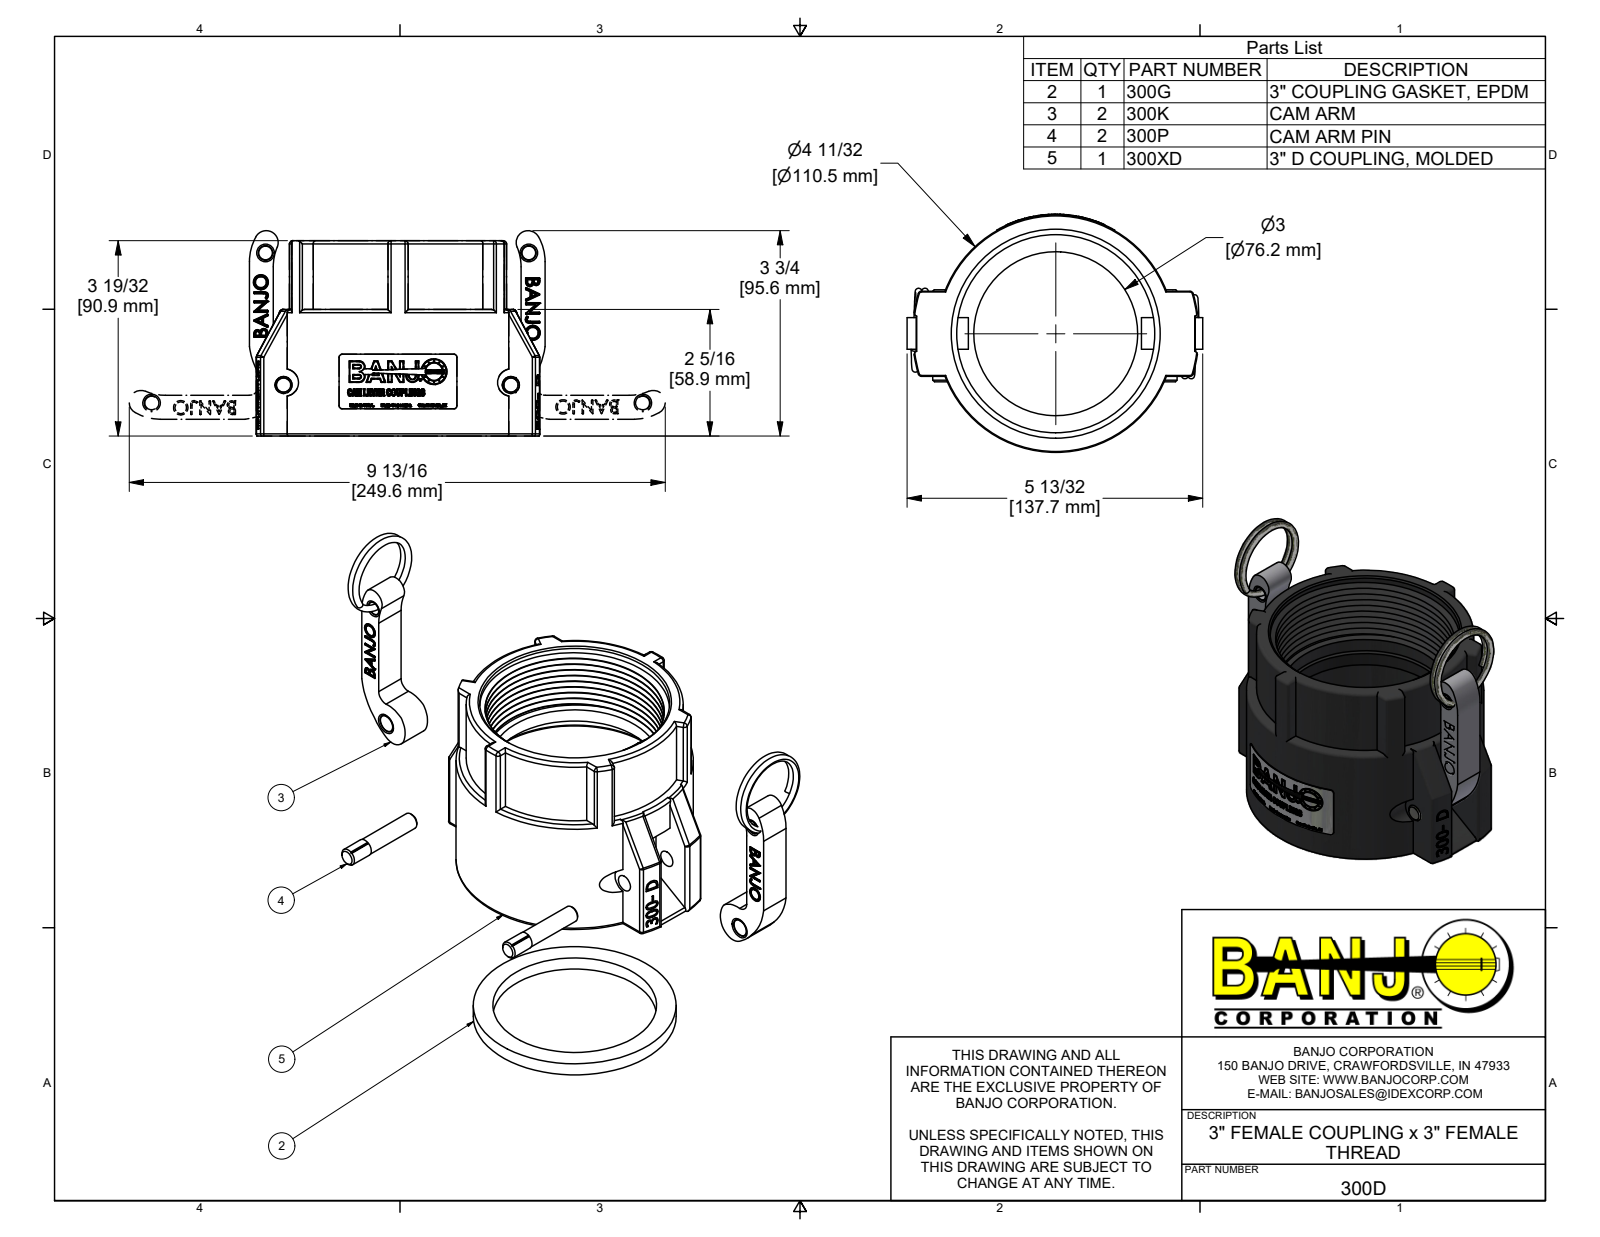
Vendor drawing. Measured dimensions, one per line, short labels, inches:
name: 300D; 300XD; 300K; 300XK (+4 more)
written by: Autodesk Inventor 2022 (AUTOMOTIVE_DESIGN)
unit: in
bodies: 9 solids, 2752 faces (909 planar, 633 cylindrical, 1210 other)
size: 5.42 × 4.774 × 4.365
volume: 20.08 in³; area: 167 in²
holes: 2× ⌀0.25, 2× ⌀0.313, 2× ⌀0.319, 1× ⌀0.318, 1× ⌀0.449, 1× ⌀3, 1× ⌀3.06, 1× ⌀3.63, 1× ⌀3.8
bosses: 2× ⌀0.325, 2× ⌀0.311, 1× ⌀4.35, 1× ⌀3.719, 1× ⌀0.473
rounds: 235× R0.006, 37× R0.06, 34× R0.005, 4× R0.929, 2× R0.028, 2× R0.039, 2× R0.05, 2× R0.093
face distances: 0.25, 1.775, 2.025, 0.46, 1.1, 0.295, 0.02, 0.27, 2.045, 0.275
hole spacings: 2.442, 5.106, 1.43, 2.77, 2.784, 3.776, 4.168, 4.825
